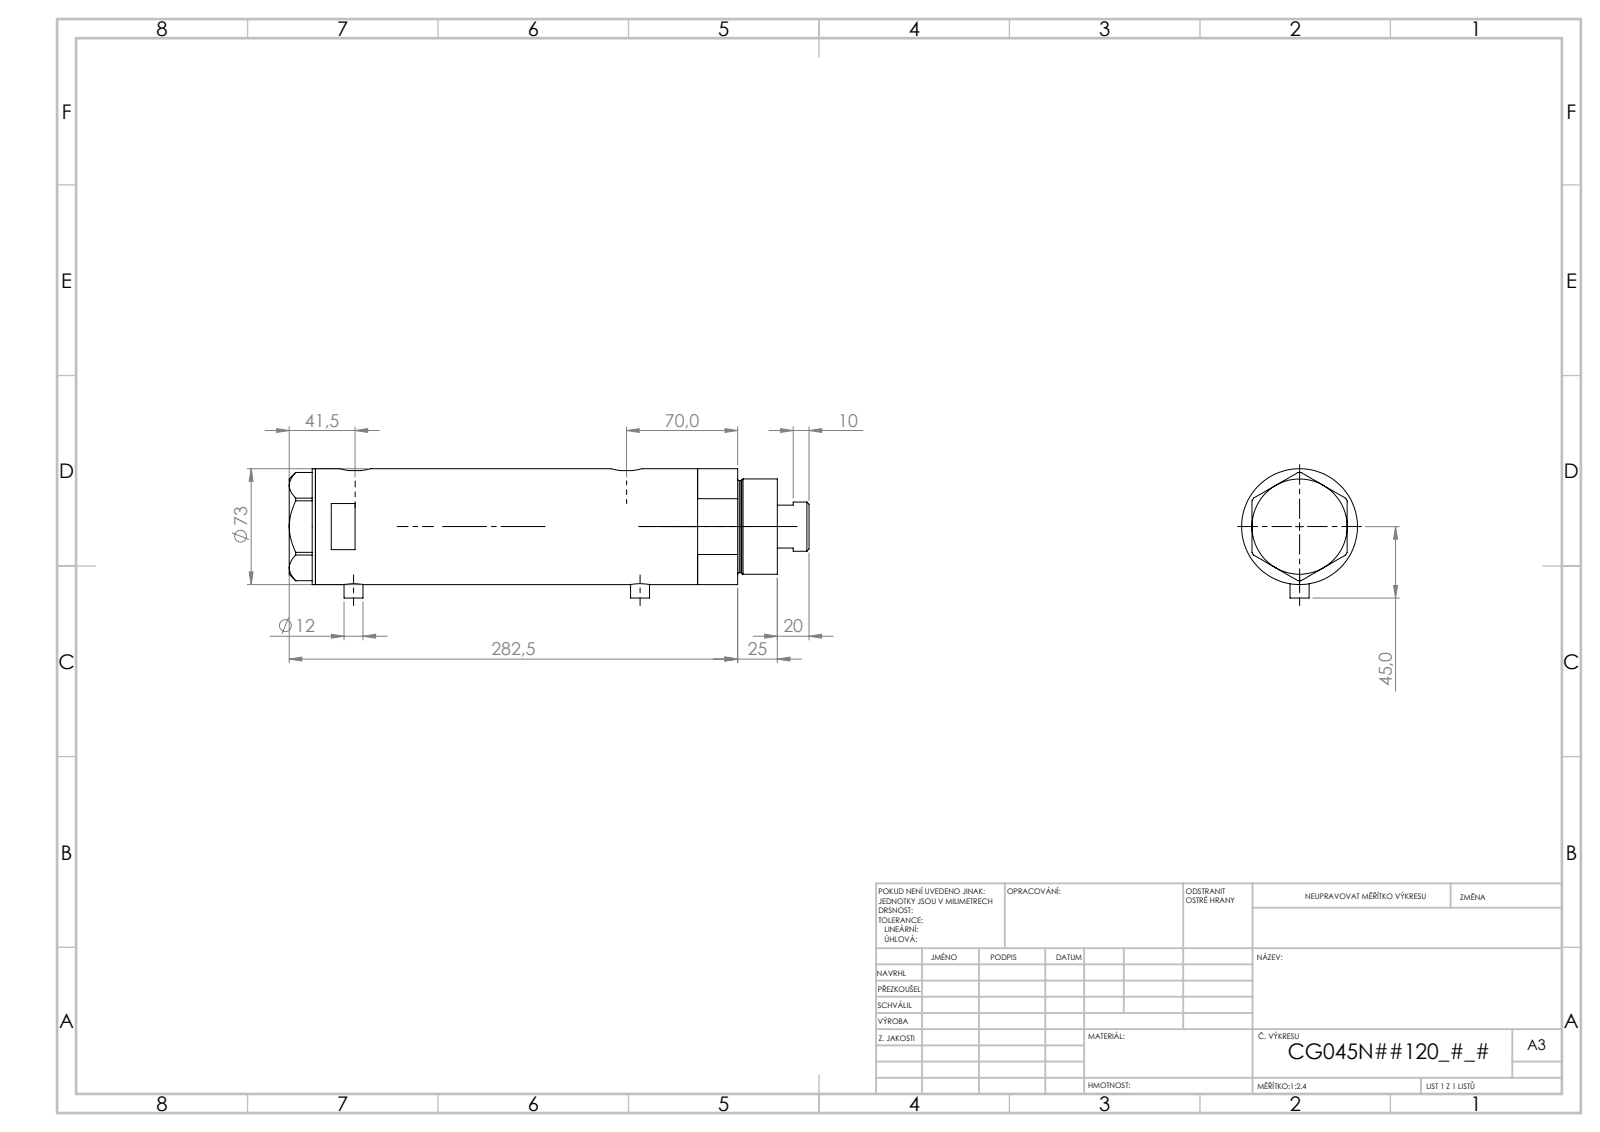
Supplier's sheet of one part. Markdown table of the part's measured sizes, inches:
| quantity | value |
| --- | --- |
| part name | V270CG_BACK; V270CG_FRONT; V270CG_MIDDLE; V270CG_VC |
| STEP written by | SolidWorks 2019 (CONFIG_CONTROL_DESIGN) |
| units | inches |
| bodies | 4 solids, 125 faces (50 planar, 55 cylindrical, 20 other) |
| overall size | 12.265 × 2.917 × 2.874 |
| volume | 65.6 in³ |
| surface area | 273.6 in² |
| round holes (diameter × count) | 0.197 × 2, 0.492 × 2, 0.518 × 2, 0.413 × 1, 1.26 × 1, 1.319 × 1, 1.772 × 1, 1.89 × 1, 2.52 × 1 |
| round bosses / shafts (diameter × count) | 0.472 × 2, 2.874 × 1, 2.362 × 1, 2.283 × 1, 1.22 × 1 |
| partial cylindrical surfaces (radius × count) | 0.394 × 2 |
| main face-to-face distances | 7.368, 1.024, 6.344, 0.65, 1.673, 8.017, 10.827, 11.477, 9.804, 3.459 |
| hole center spacings | 6.758, 0.039, 0.039, 0.335, 0.335, 6.384, 6.423, 6.423 |
